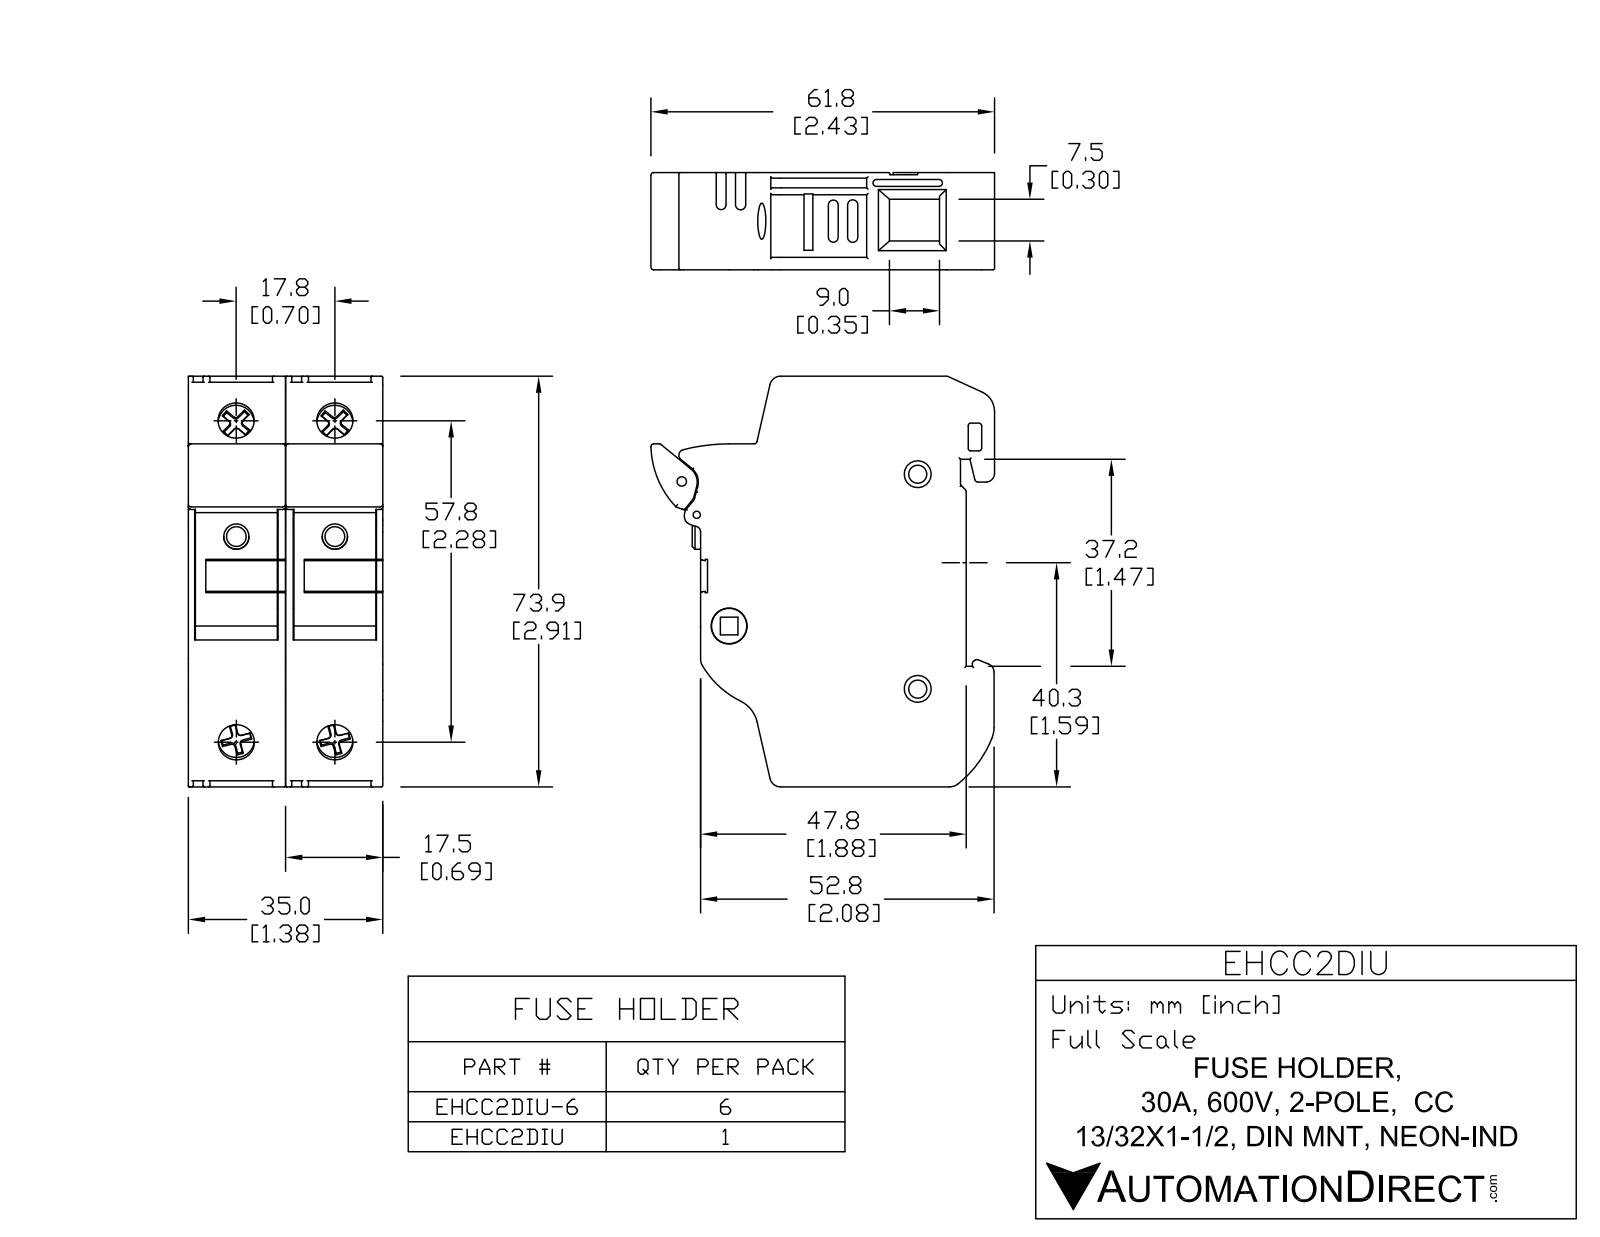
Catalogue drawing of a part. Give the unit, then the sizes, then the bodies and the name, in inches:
Units: inches
Overall size (bounding box): 2.909 × 2.434 × 1.378
Round holes (diameter × count): ⌀0.256 ×4, ⌀0.128 ×2, ⌀0.19 ×2, ⌀0.051 ×1, ⌀0.067 ×1, ⌀0.255 ×1
Round bosses / shafts (diameter × count): ⌀0.179 ×2, ⌀0.25 ×1
Partial cylindrical surfaces — rounded edges, fillets, slot ends (radius × count): R0.01 ×99, R0.02 ×11, R0.079 ×10, R0.02 ×9, R0.025 ×8, R0.039 ×7, R0.035 ×6, R0.036 ×6
Main face-to-face distances: 0.689, 1.378, 0.049, 0.062, 0.64, 1.083, 1.145, 0.903, 0.973, 0.016
Hole centre spacings: 0.689, 0.259, 0.82, 1.077, 1.408, 1.409, 1.52, 1.522
Volume: 6.437 in³ · Surface area: 52.66 in²
Bodies: 1 solid, 1062 faces (497 planar, 333 cylindrical, 232 other)
Part name (STEP PRODUCT): EHCC2DIU
STEP written by: SolidWorks 2017 (AUTOMOTIVE_DESIGN)
